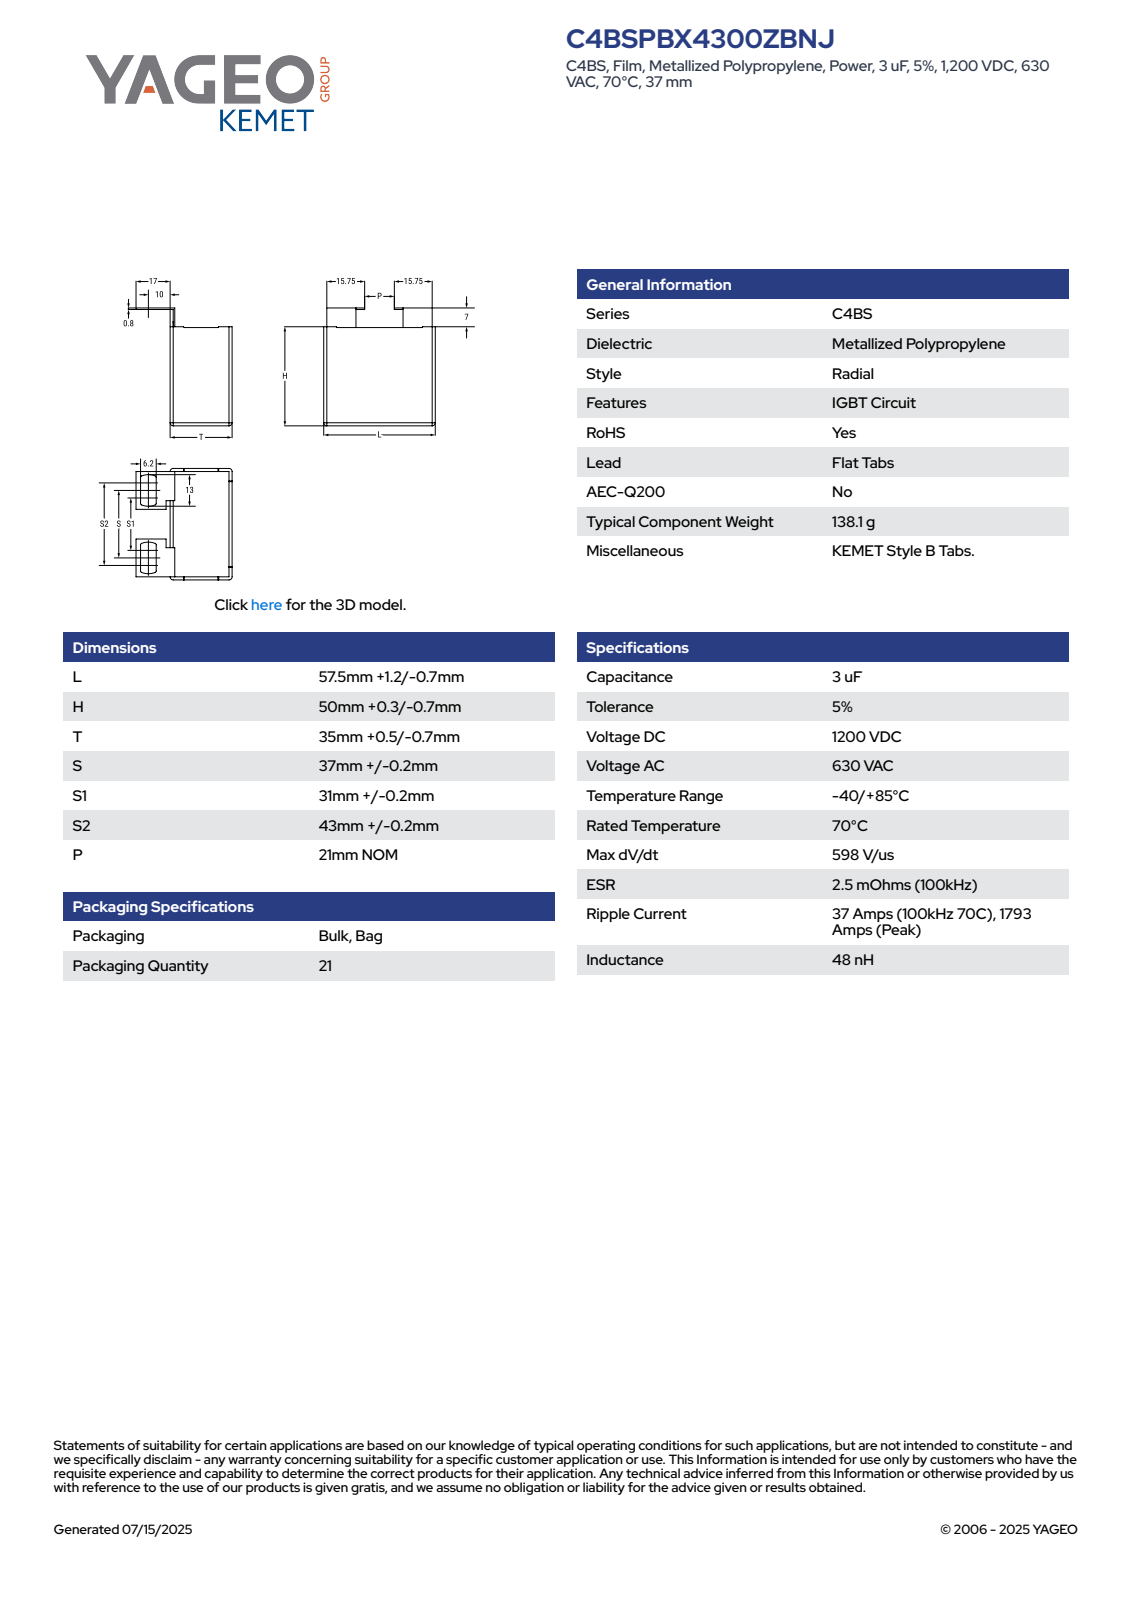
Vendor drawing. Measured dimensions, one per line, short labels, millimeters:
name: CFP_C4BB_57.5X50X35_L58.7H50.3T35.5S37.2
written by: SolidWorks 2014 (AUTOMOTIVE_DESIGN)
unit: mm
bodies: 4 solids, 93 faces (85 planar, 8 cylindrical, 0 other)
size: 58.7 × 57.3 × 52.5
volume: 105 353 mm³; area: 15 335 mm²
rounds: 4× R4.6, 2× R0.2
face distances: 35.5, 50.3, 58.7, 0.8, 57.3, 7, 6.2, 56.5, 33.5, 2
